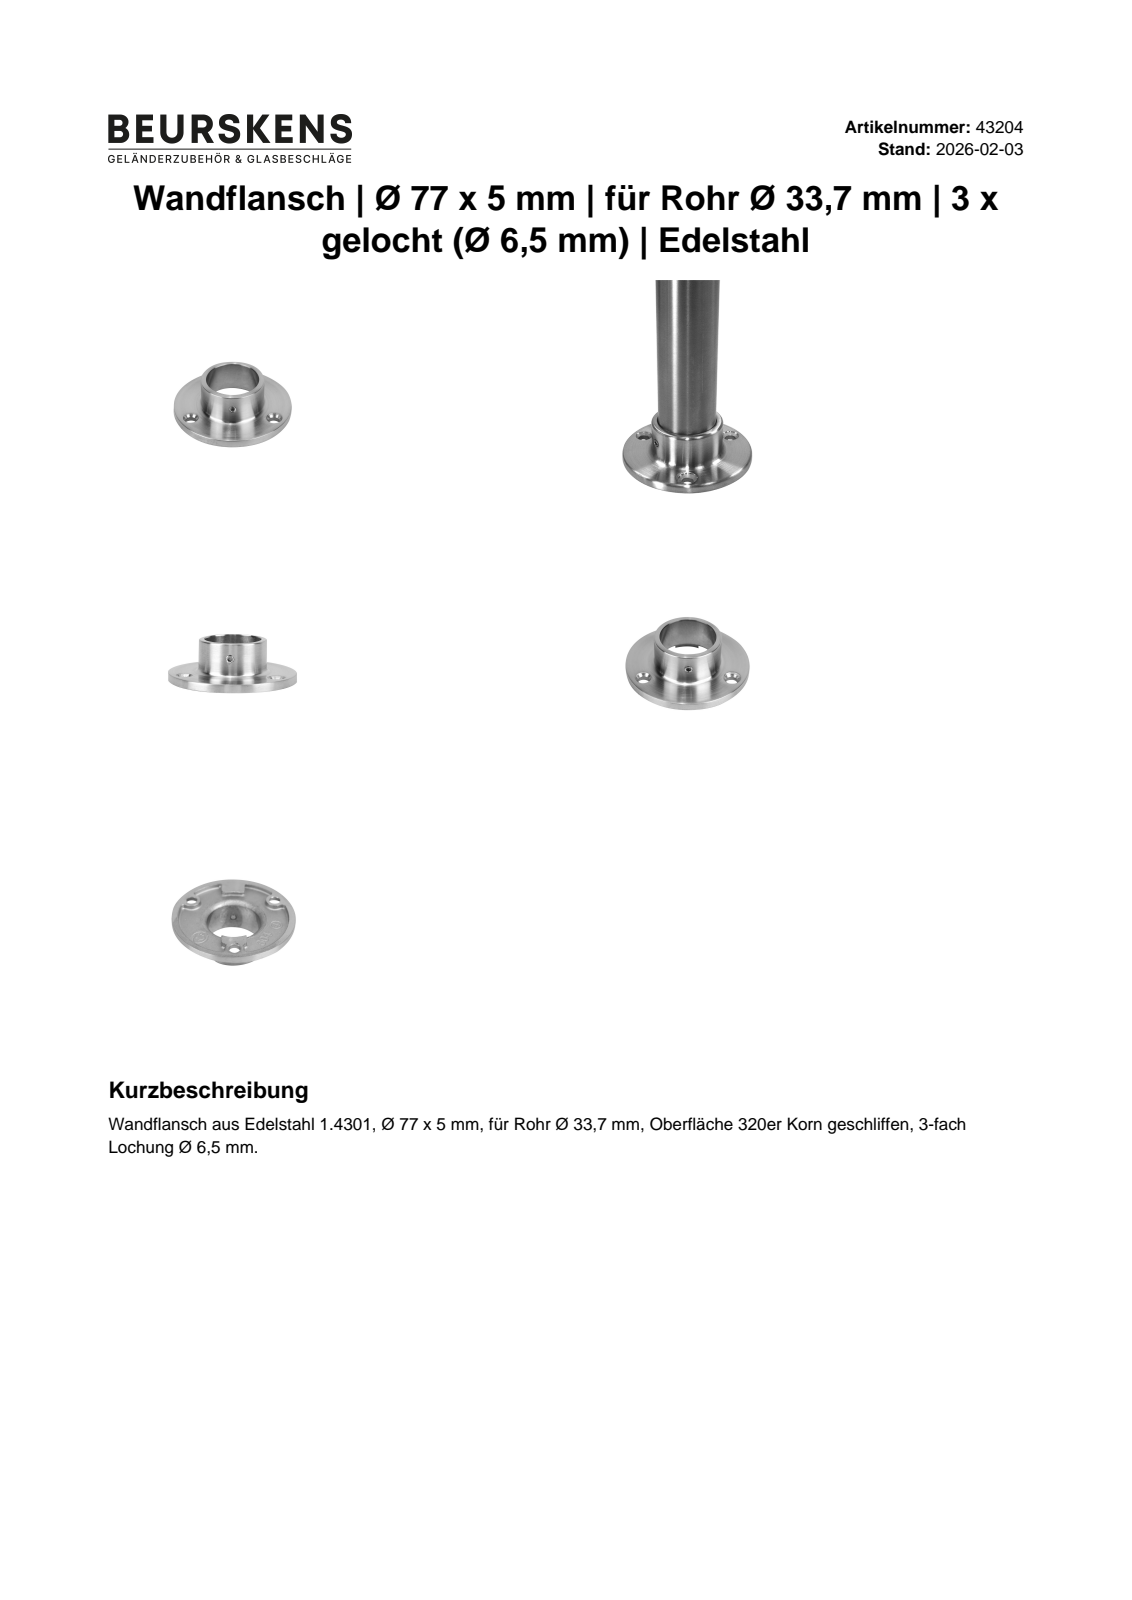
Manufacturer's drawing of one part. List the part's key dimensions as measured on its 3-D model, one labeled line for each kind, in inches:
Part name (STEP PRODUCT): 43204
STEP written by: Autodesk Inventor 2022 (AUTOMOTIVE_DESIGN)
Units: inches
Bodies: 1 solid, 15 faces (3 planar, 7 cylindrical, 5 other)
Overall size (bounding box): 3.031 × 3.031 × 0.984
Volume: 1.624 in³ · Surface area: 21.5 in²
Round holes (diameter × count): ⌀0.256 ×3, ⌀0.157 ×1, ⌀1.327 ×1
Round bosses / shafts (diameter × count): ⌀3.031 ×1, ⌀1.614 ×1
Main face-to-face distances: 0.197, 0.984, 0.787
Hole centre spacings: 1.24, 2.148
